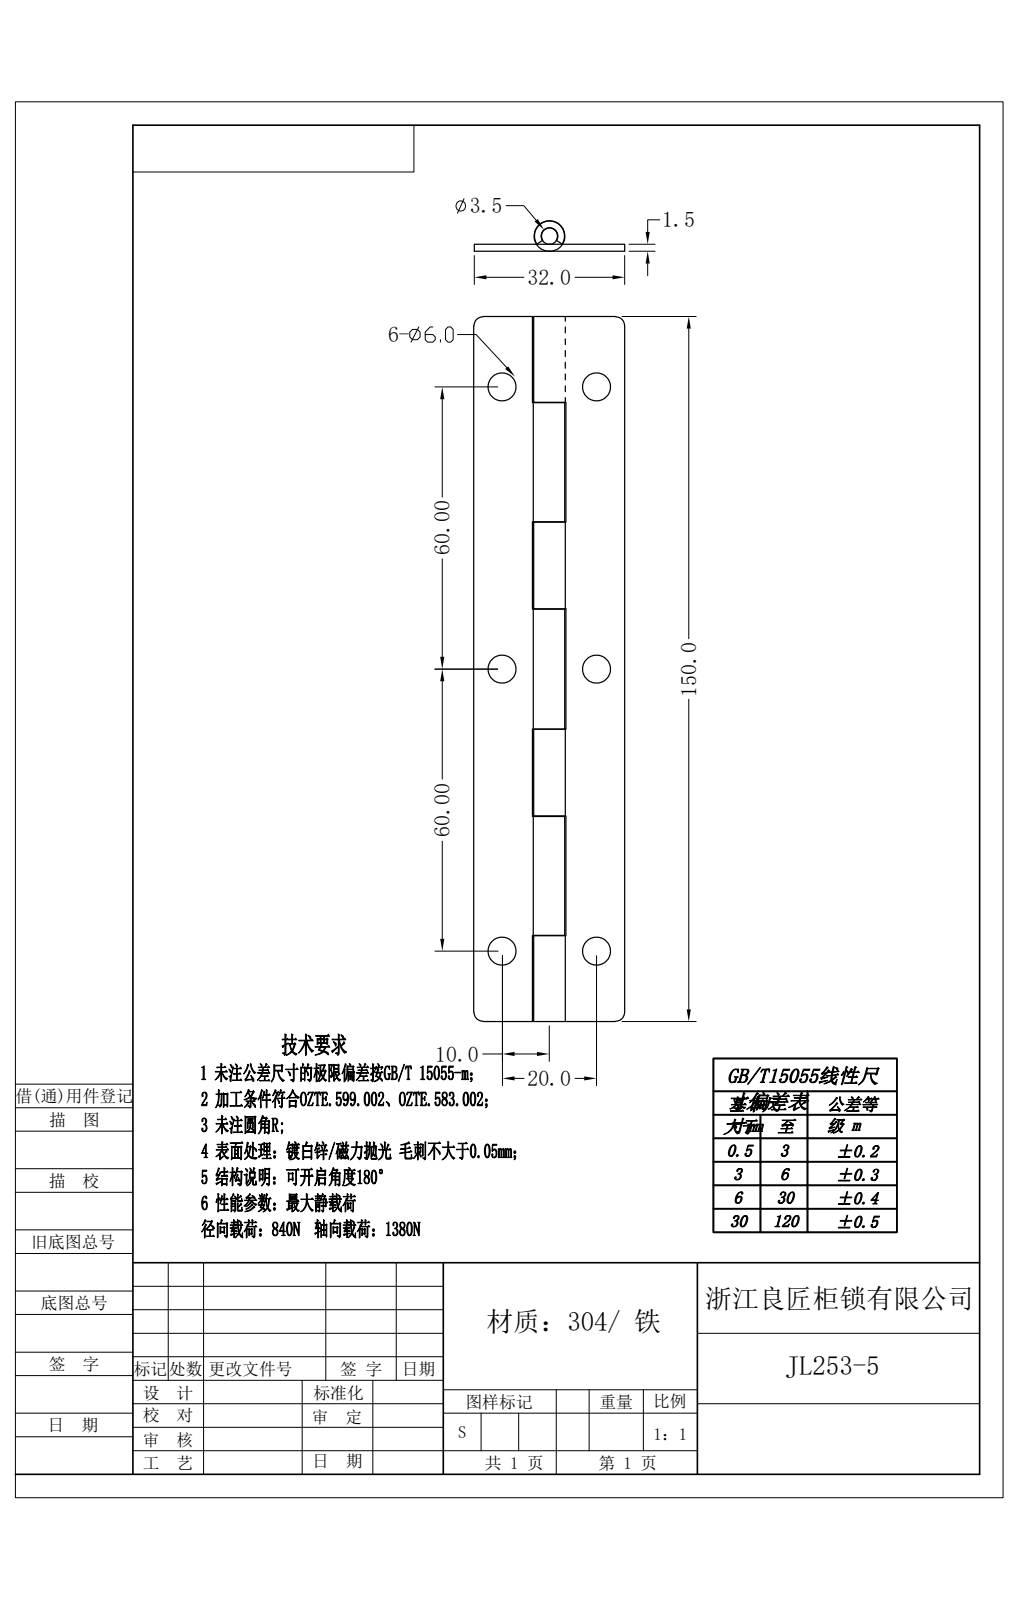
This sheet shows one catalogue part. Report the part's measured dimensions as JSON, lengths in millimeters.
{"step_written_by": "Rhino 8.5 (CONFIG_CONTROL_DESIGN)", "units": "millimeters", "bodies": {"solids": 3, "faces": 70, "planar": 38, "cylindrical": 32, "other": 0}, "overall_size": [150, 32, 6.5], "volume_mm3": 10300, "surface_area_mm2": 15140, "round_holes": [[6, 6], [3.5, 1]], "round_bosses_or_shafts": [[6.5, 1], [3.2, 1]], "partial_cylinders_radius": [[2, 4]], "face_to_face_distances": [1.5, 32, 19.6, 12.4, 12.5, 7.1, 19.5, 88, 25.4, 44], "hole_center_spacings": [60, 63.25, 20, 120, 121.66]}
